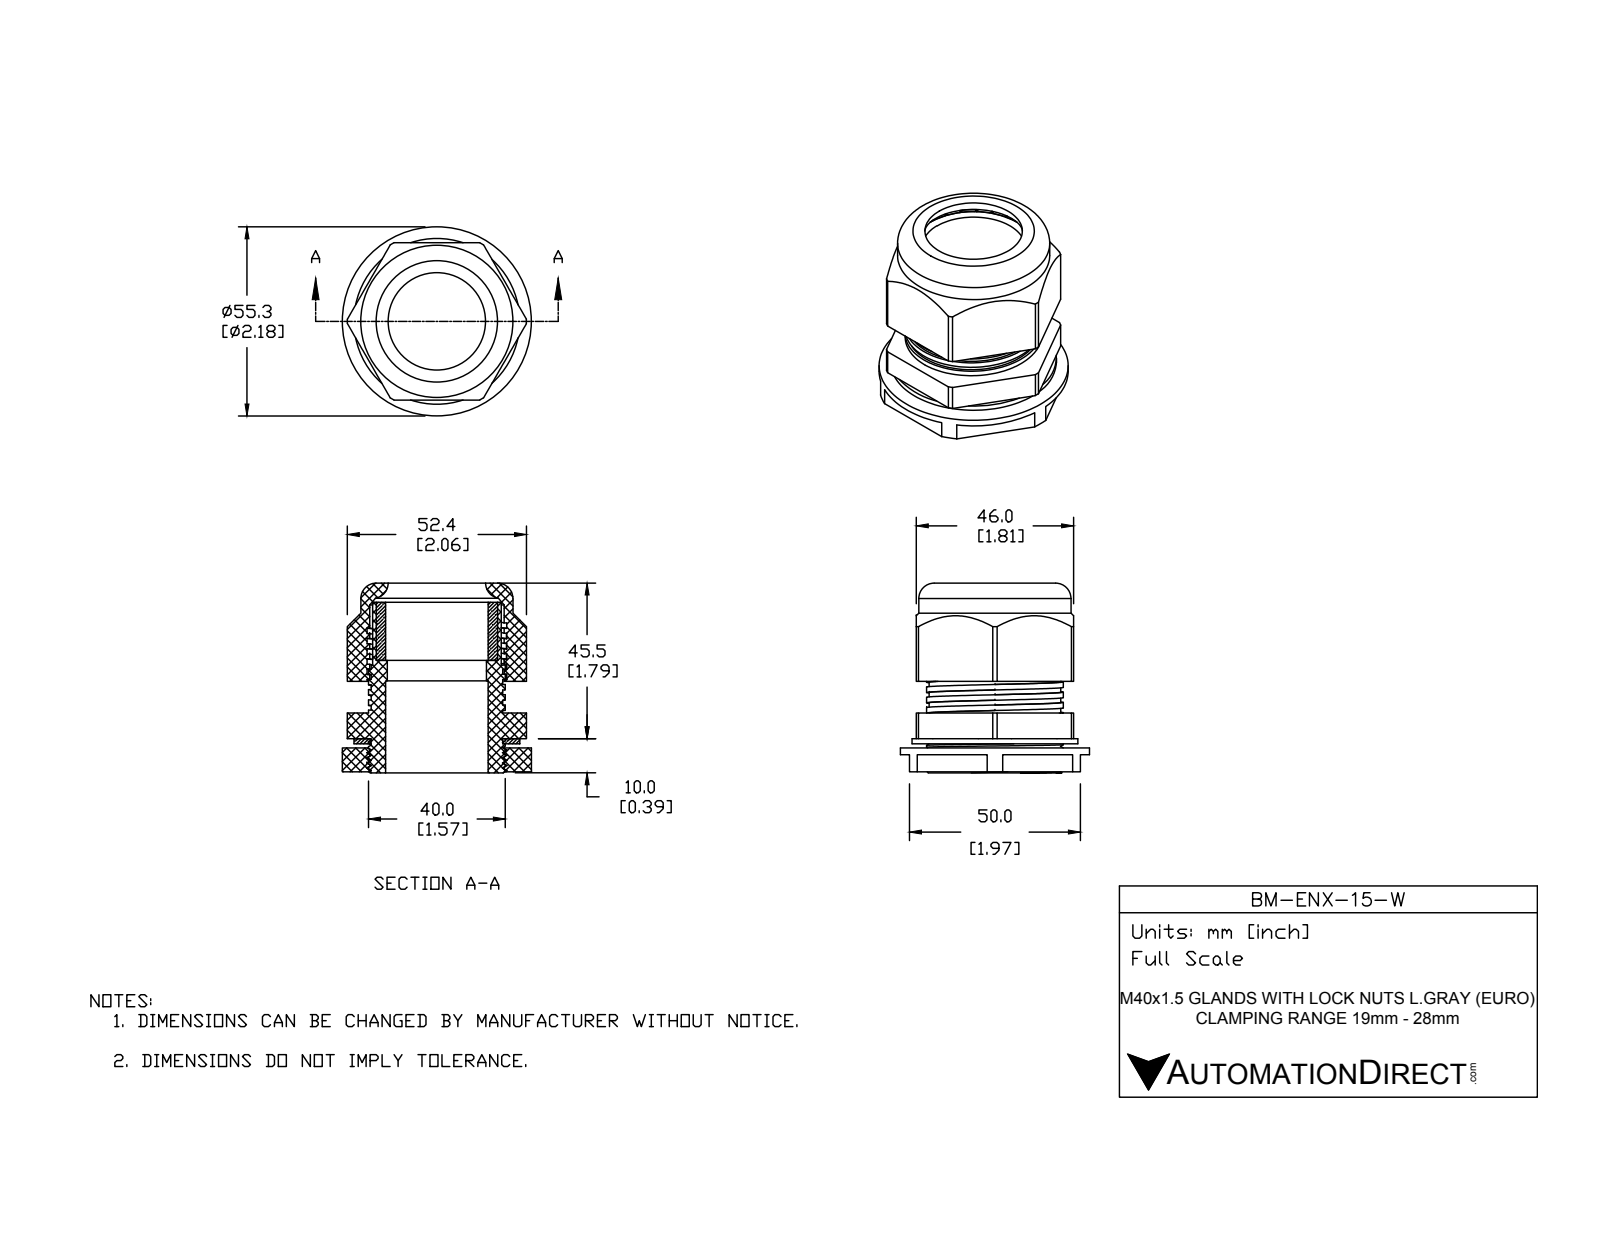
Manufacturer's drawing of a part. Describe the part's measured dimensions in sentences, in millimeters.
The part is named "BM-ENX-15-W". Its 3-D file was written by "SolidWorks 2015 (CONFIG_CONTROL_DESIGN)". It is 5 solids with 242 faces: 139 planar, 82 cylindrical and 21 other. Overall it measures 55.5 by 55.3 by 55.3 millimeters. Its volume is 51 922 cubic millimeters and its surface area 36 919 square millimeters. Round holes: 1 of diameter 29, 1 of diameter 30, 1 of diameter 35.5, 1 of diameter 38.5, 1 of diameter 39.33. Round bosses or shafts: 1 of diameter 55.3, 1 of diameter 48.5, 1 of diameter 44.5, 1 of diameter 40, 1 of diameter 37.6. Partial cylindrical surfaces (rounded edges, fillets, slot ends): 1 of radius 26.2. The main face-to-face distances are 46, 2.69, 2, 7, 9.69, 48, 8.19, 1.19, 1.5, 17.19.
